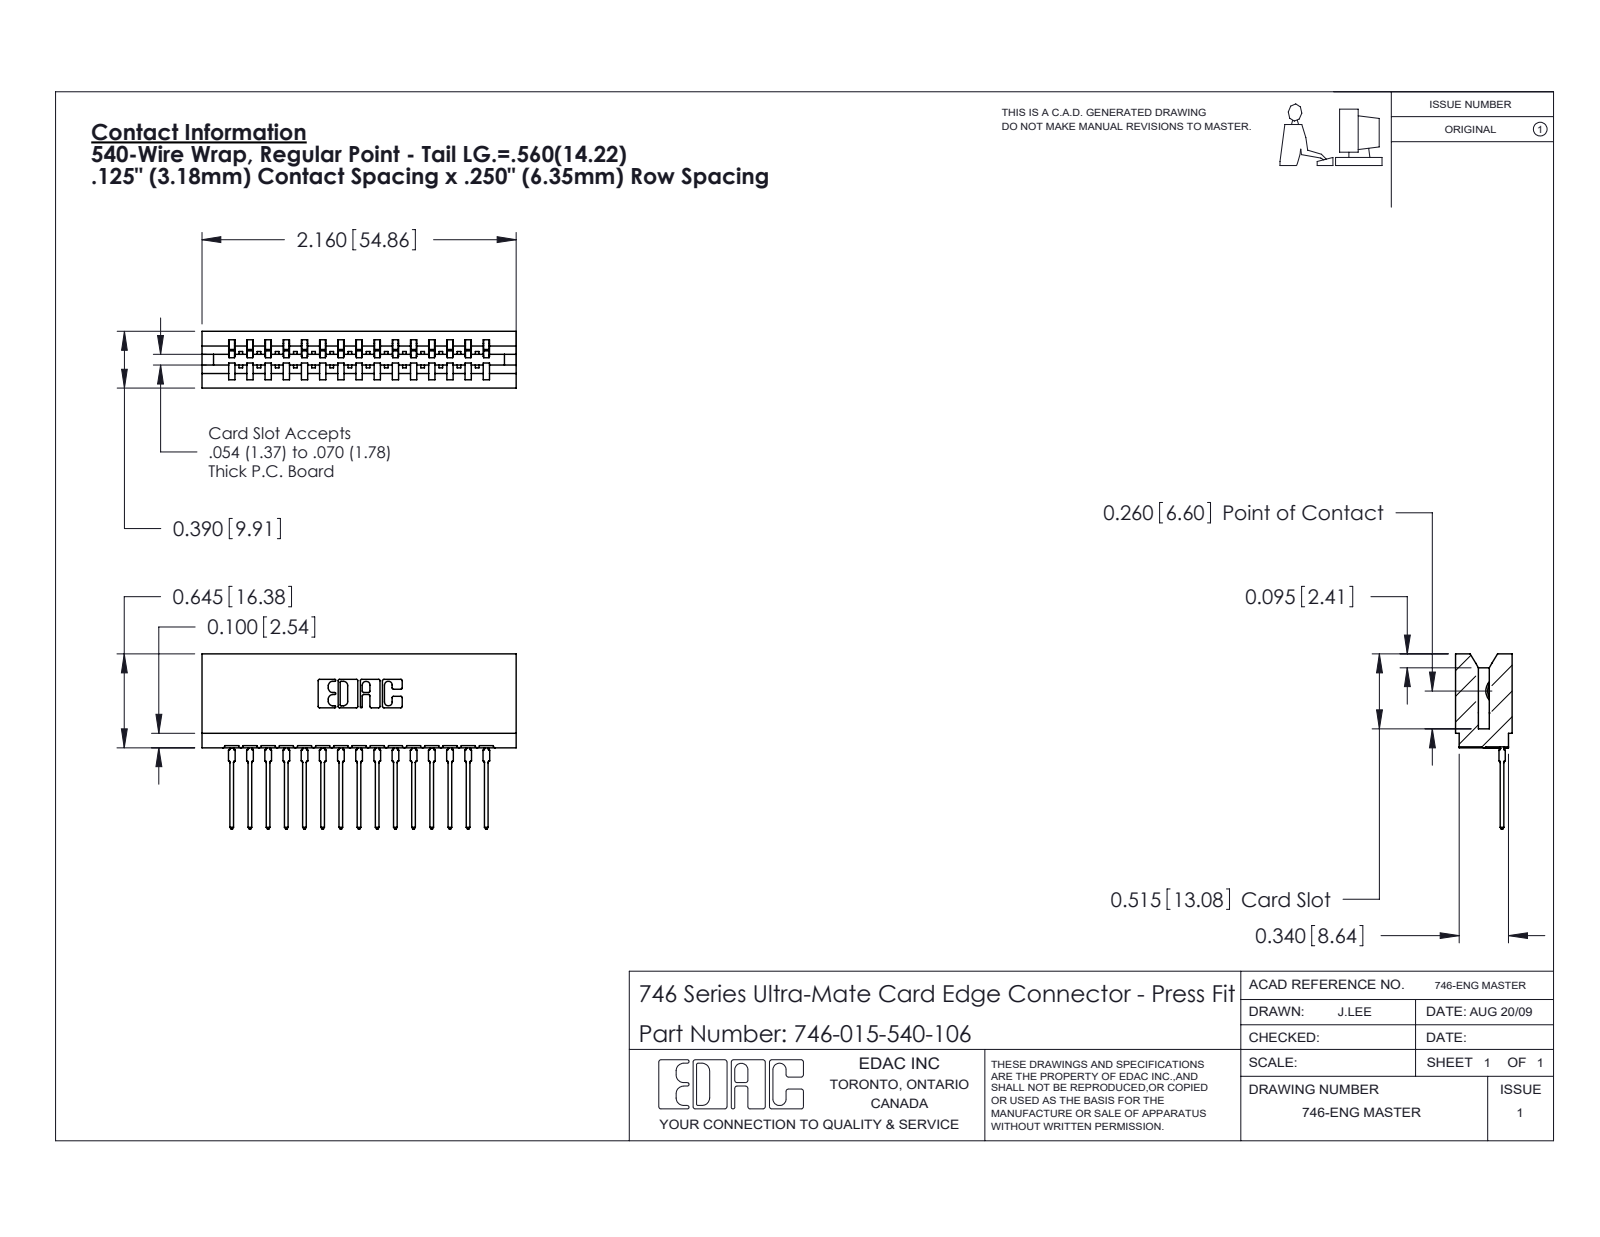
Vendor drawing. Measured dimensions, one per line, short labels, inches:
name: 746-292-001_540; 746 Part_.515 Slot Depth - 06; 746-015-540-106
written by: SolidWorks 2020 (CONFIG_CONTROL_DESIGN)
unit: in
bodies: 16 solids, 1718 faces (1001 planar, 327 cylindrical, 390 other)
size: 2.16 × 1.204 × 0.39
volume: 0.362 in³; area: 13.22 in²
rounds: 30× R0.021, 22× R0.01, 16× R0.015, 6× R0.007, 6× R0.031, 4× R0.005, 4× R0.011, 3× R0.026
face distances: 0.25, 0.057, 0.333, 0.5, 0.39, 0.042, 0.125, 0.208, 0.125, 0.025
